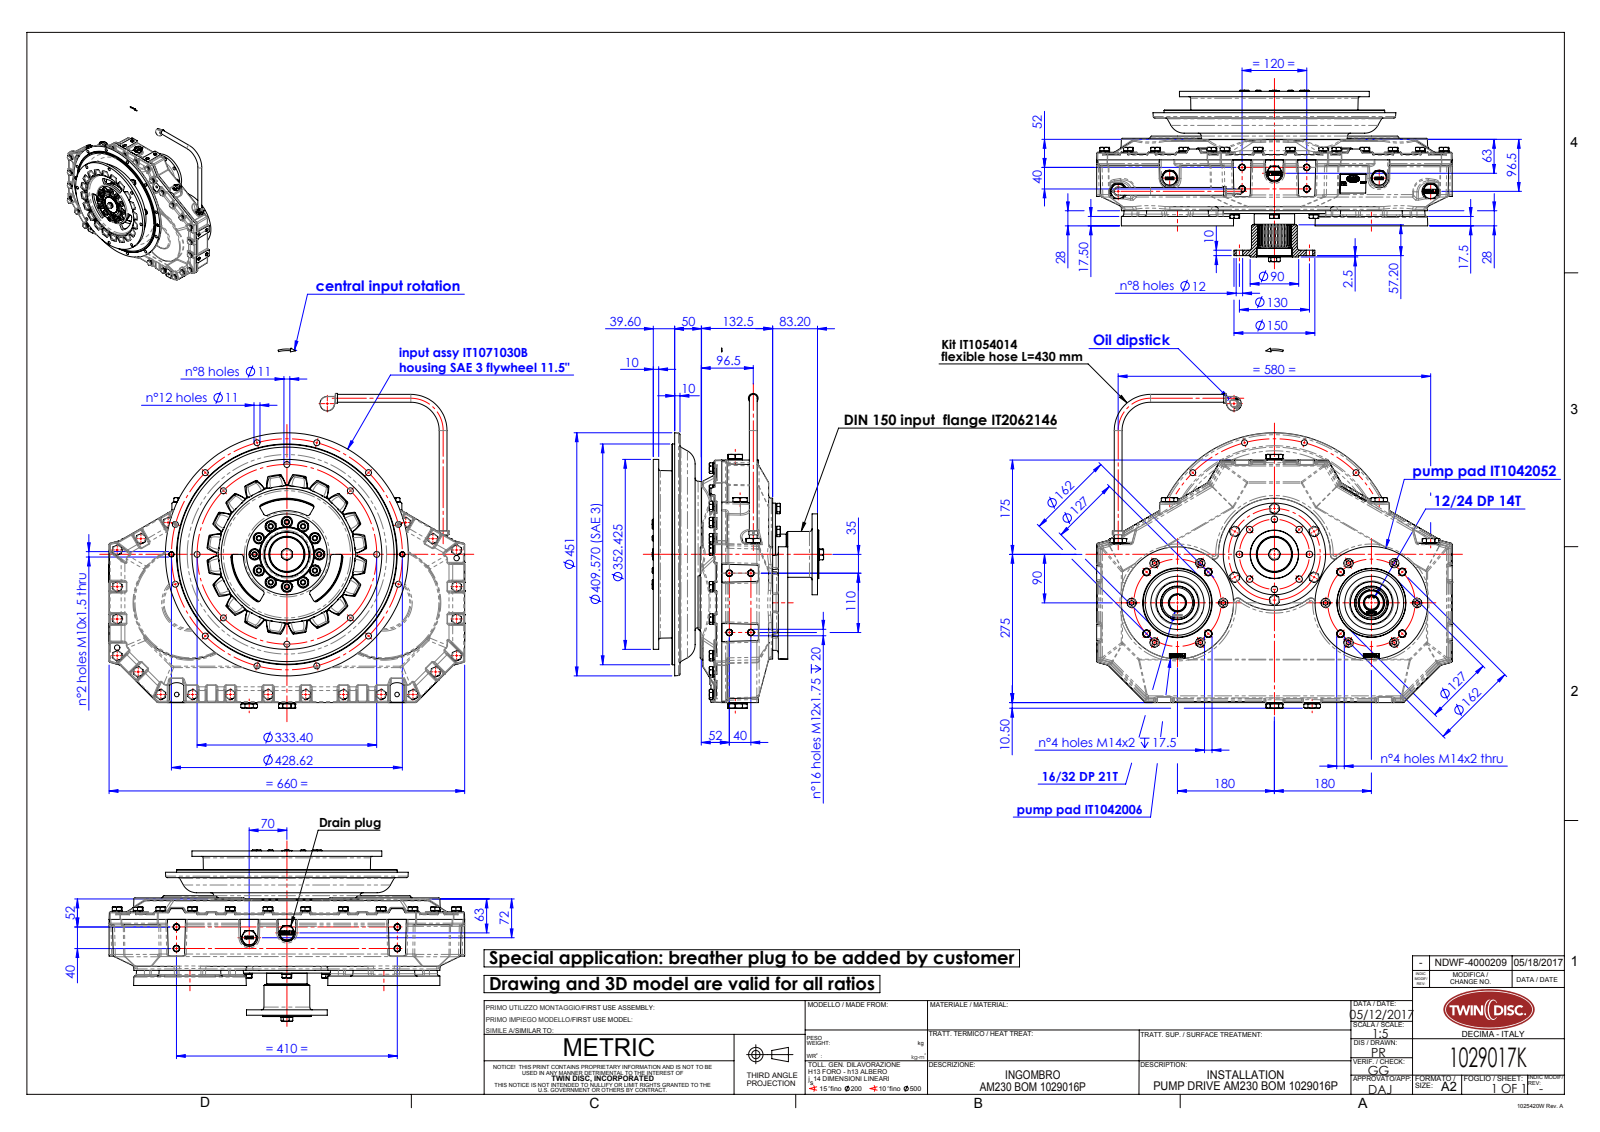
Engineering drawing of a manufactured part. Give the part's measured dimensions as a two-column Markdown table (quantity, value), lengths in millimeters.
| quantity | value |
| --- | --- |
| part name | 1029017K; ITam230-018_rev00-installation; IT1054022_rev00-installation; IT1071030B_rev03-installation (+8 more) |
| STEP written by | SolidWorks 2015 (AUTOMOTIVE_DESIGN) |
| units | millimeters |
| bodies | 41 solids, 8810 faces (3384 planar, 2614 cylindrical, 2812 other) |
| overall size | 668.04 × 660 × 318.2 |
| volume | 7 288 000 mm³ |
| surface area | 3 326 000 mm² |
| round holes (diameter × count) | 10.5 × 58, 10.2 × 44, 8.5 × 32, 12 × 28, 11 × 24, 17 × 12, 10 × 10, 14 × 8, 12.2 × 7, 13 × 7, 8 × 4, 18.5 × 3 |
| round bosses / shafts (diameter × count) | 10 × 62, 16.2 × 48, 18.1 × 35, 21 × 12, 16 × 12, 18 × 8, 21.1 × 7, 12 × 7 |
| partial cylindrical surfaces (radius × count) | 2 × 201, 3 × 156, 2.5 × 118, 5 × 86, 1 × 82, 4 × 80, 0.45 × 58, 26.41 × 58 |
| main face-to-face distances | 40, 5, 21, 94.5, 28, 26, 19, 143.5, 115.5, 17.5 |
| hole center spacings | 120, 57.4, 75, 138.58, 40, 207.84, 22.59, 51.37 |
